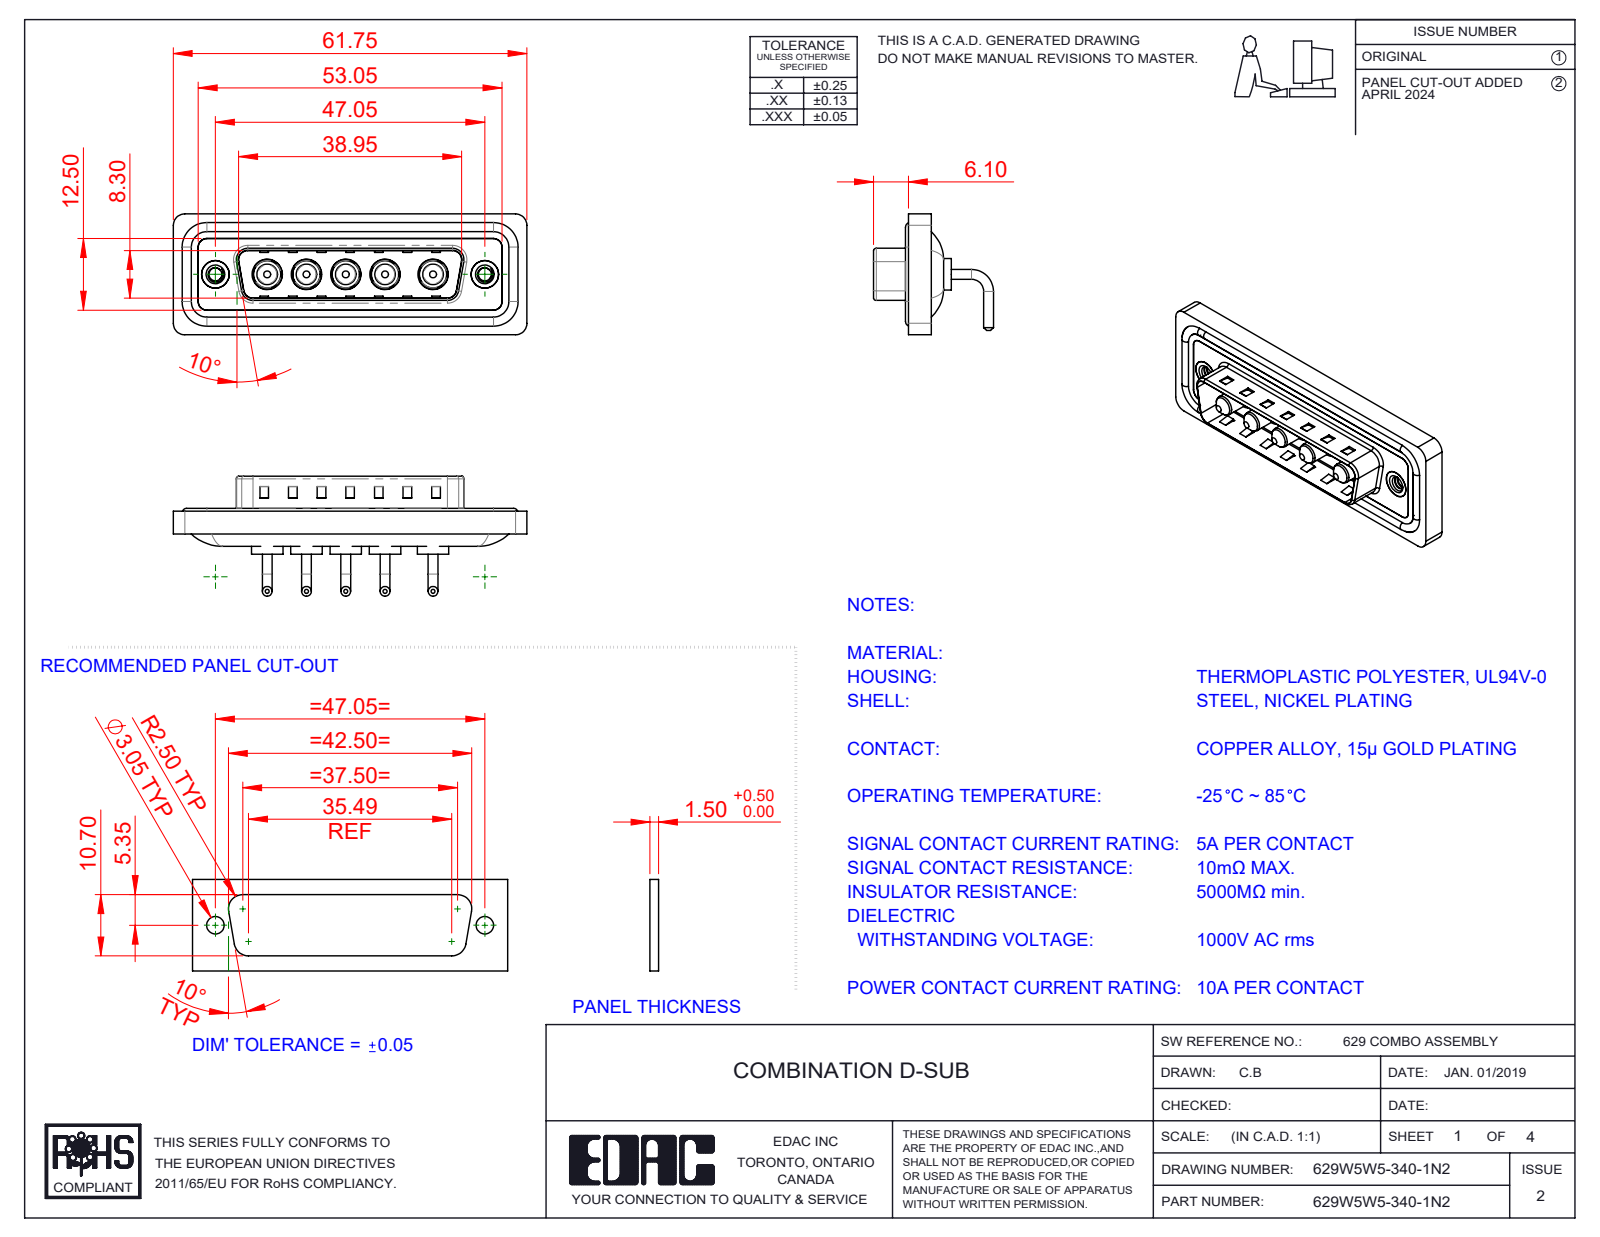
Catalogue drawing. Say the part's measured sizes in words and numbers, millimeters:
The part is named "629Combo Shell Rear_25 Contacts; 629Combo Housing_5W5; Power Pin_10A RA; 629Combo Threaded Rivet_2 (+3 more)". Its 3-D file was written by "SolidWorks 2023 (CONFIG_CONTROL_DESIGN)". It is 17 solids with 698 faces: 259 planar, 293 cylindrical and 146 other. Overall it measures 61.75 by 21.1 by 20.95 millimeters. Its volume is 7 523 cubic millimeters and its surface area 12 018 square millimeters. Round holes: 5 of diameter 4.85, 5 of diameter 5.3, 2 of diameter 2.26, 2 of diameter 4, 2 of diameter 4.8, 2 of diameter 5. Round bosses or shafts: 10 of diameter 1.7, 5 of diameter 5.5, 5 of diameter 5.2, 5 of diameter 4.75, 5 of diameter 3.75, 5 of diameter 3.6, 4 of diameter 1.6, 2 of diameter 4.9. Partial cylindrical surfaces (rounded edges, fillets, slot ends): 18 of radius 1.5, 18 of radius 2, 8 of radius 0.5, 8 of radius 1.6, 5 of radius 2.1, 4 of radius 0.25, 4 of radius 0.6, 4 of radius 0.65. The main face-to-face distances are 0.4, 2.9, 0.8, 4.5, 4.1, 1.5, 1.1, 2.1, 3.1, 6. The hole center spacings are 6.86, 13.73, 6.85, 6.87, 8.37, 8.38, 9.04, 9.05.
